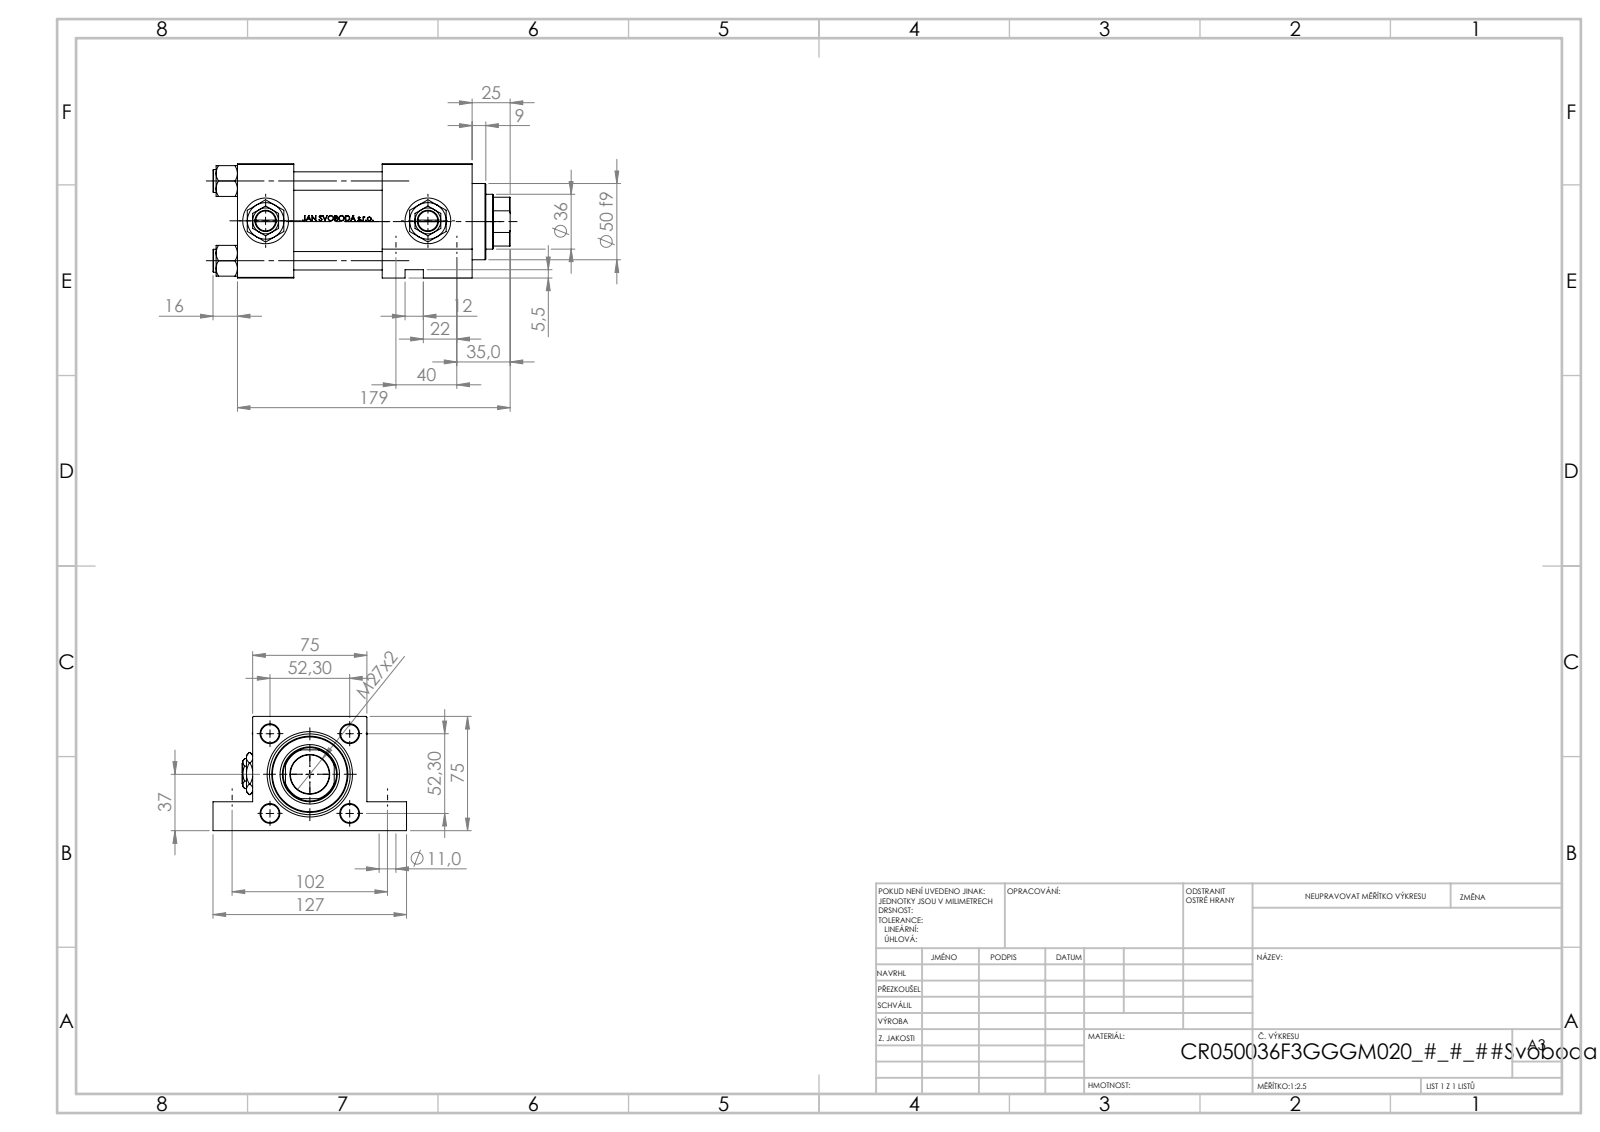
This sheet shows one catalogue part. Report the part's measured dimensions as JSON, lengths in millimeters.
{"part_name": "V215CR_F_Body; V215CR_VCP_F; V215CR_F_TYCINKA; V215_VC_A (+2 more)", "step_written_by": "SolidWorks 2019 (CONFIG_CONTROL_DESIGN)", "units": "millimeters", "bodies": {"solids": 13, "faces": 1202, "planar": 484, "cylindrical": 136, "other": 582}, "overall_size": [195, 127, 75], "volume_mm3": 729885, "surface_area_mm2": 168973, "round_holes": [[12, 4], [20.96, 4], [30, 4], [7, 3], [11, 2], [11, 2], [25.5, 1], [36, 1], [39, 1], [41, 1], [53, 1]], "round_bosses_or_shafts": [[15, 4], [56, 1], [50, 1]], "partial_cylinders_radius": [[17.5, 1]], "face_to_face_distances": [75, 37, 58, 95, 59, 154, 117, 19, 56, 74.8], "hole_center_spacings": [52.3, 36.63, 37.34, 40, 51.62, 60.21, 73.96, 99.56]}
